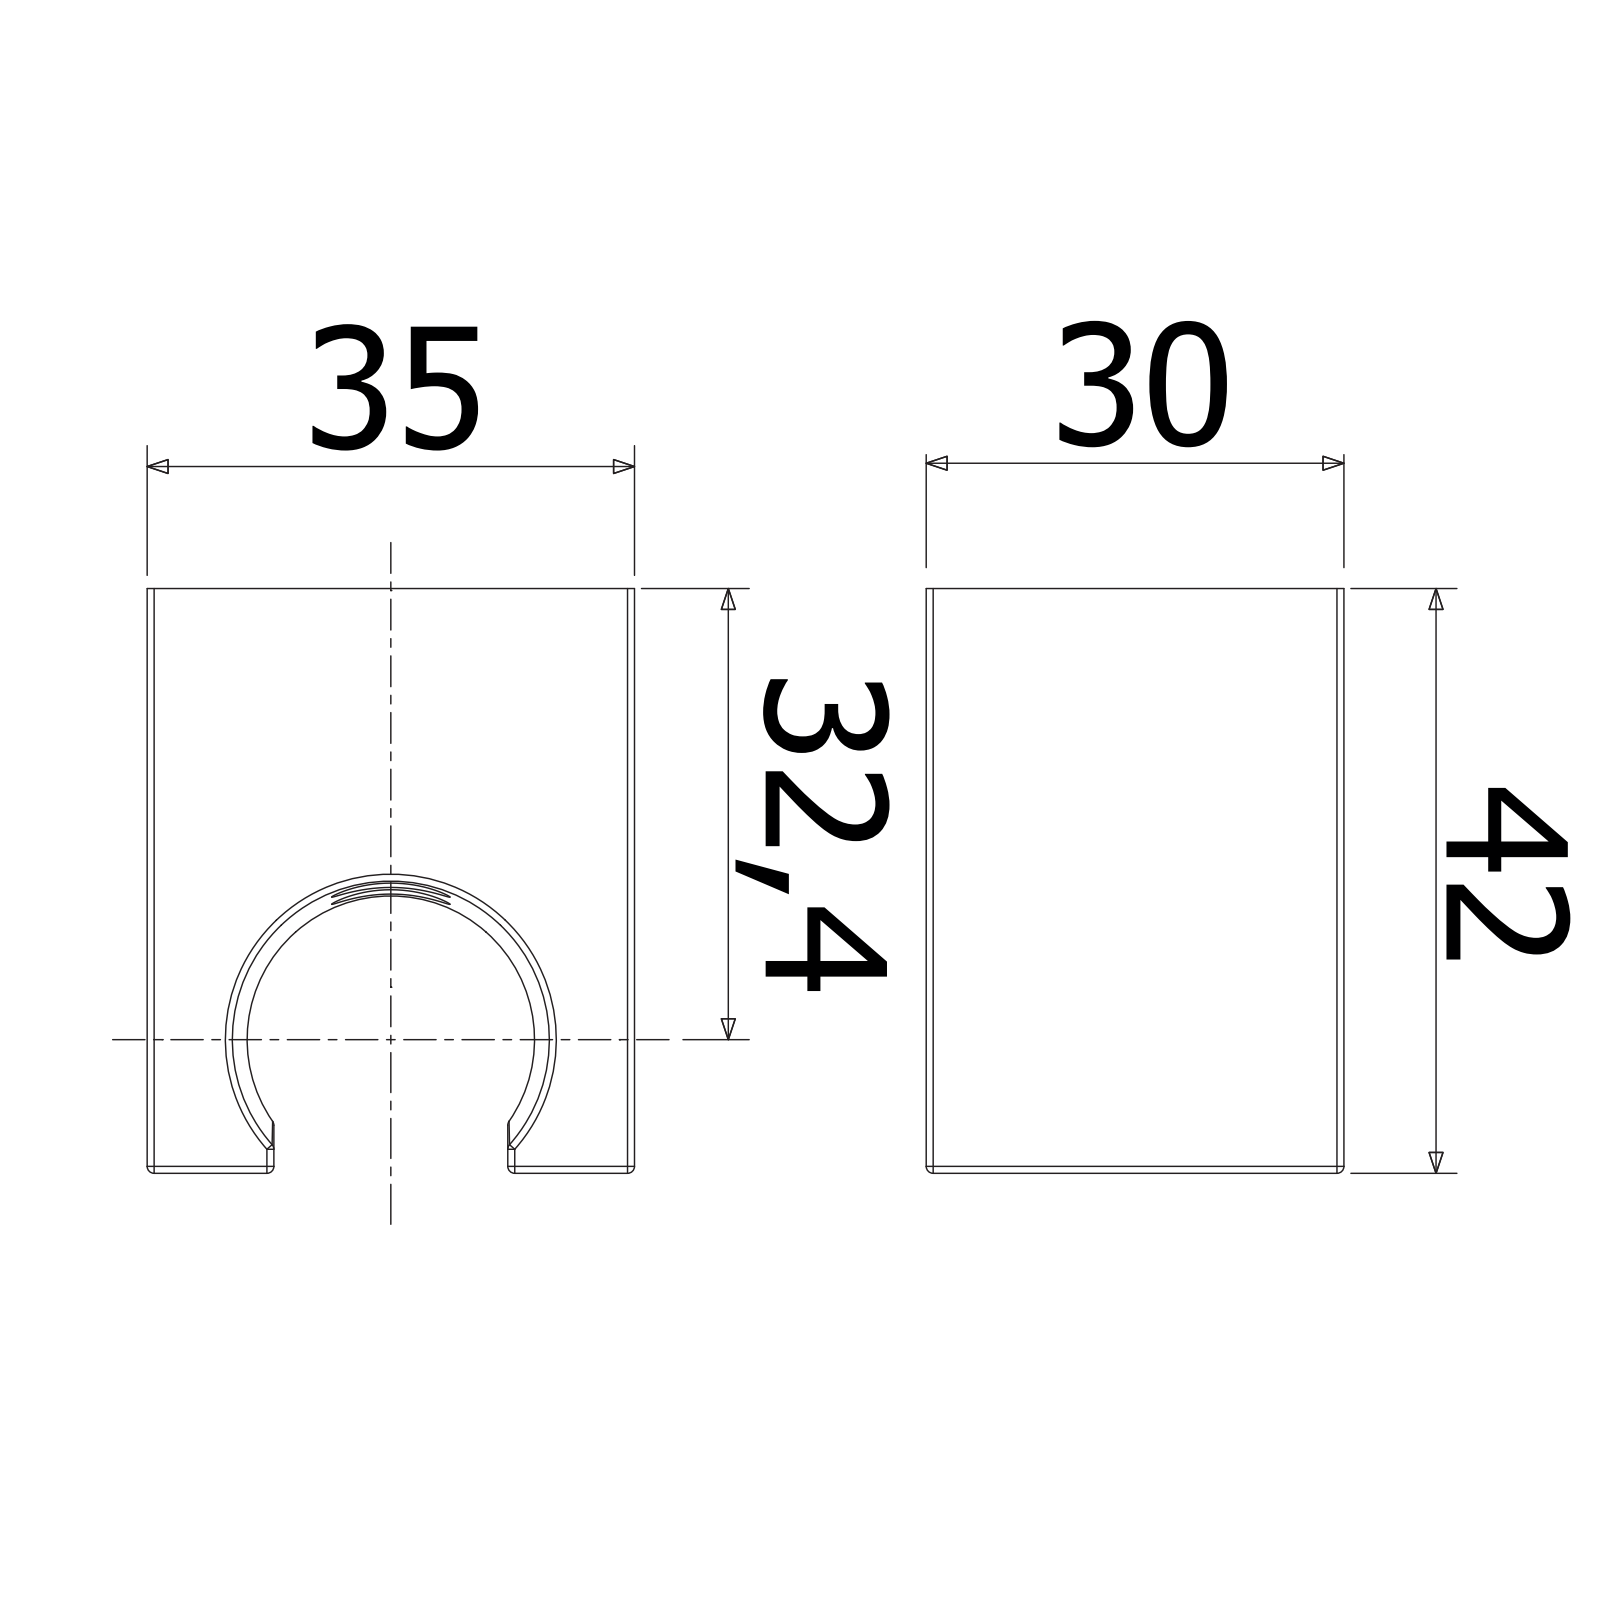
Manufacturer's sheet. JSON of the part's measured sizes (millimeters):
{"part_name": "ZSUP026CR", "step_written_by": "CREO PARAMETRIC BY PTC INC, 2020044 (CONFIG_CONTROL_DESIGN)", "units": "millimeters", "bodies": {"solids": 0, "faces": 67, "planar": 21, "cylindrical": 28, "other": 18}, "overall_size": [42, 35, 30], "round_holes": [[4.75, 2], [8.5, 2]], "round_bosses_or_shafts": [[10, 2]], "partial_cylinders_radius": [[0.5, 14]], "face_to_face_distances": [2, 33, 28, 35, 30, 31, 26, 42, 40, 7.1], "hole_center_spacings": [13]}
